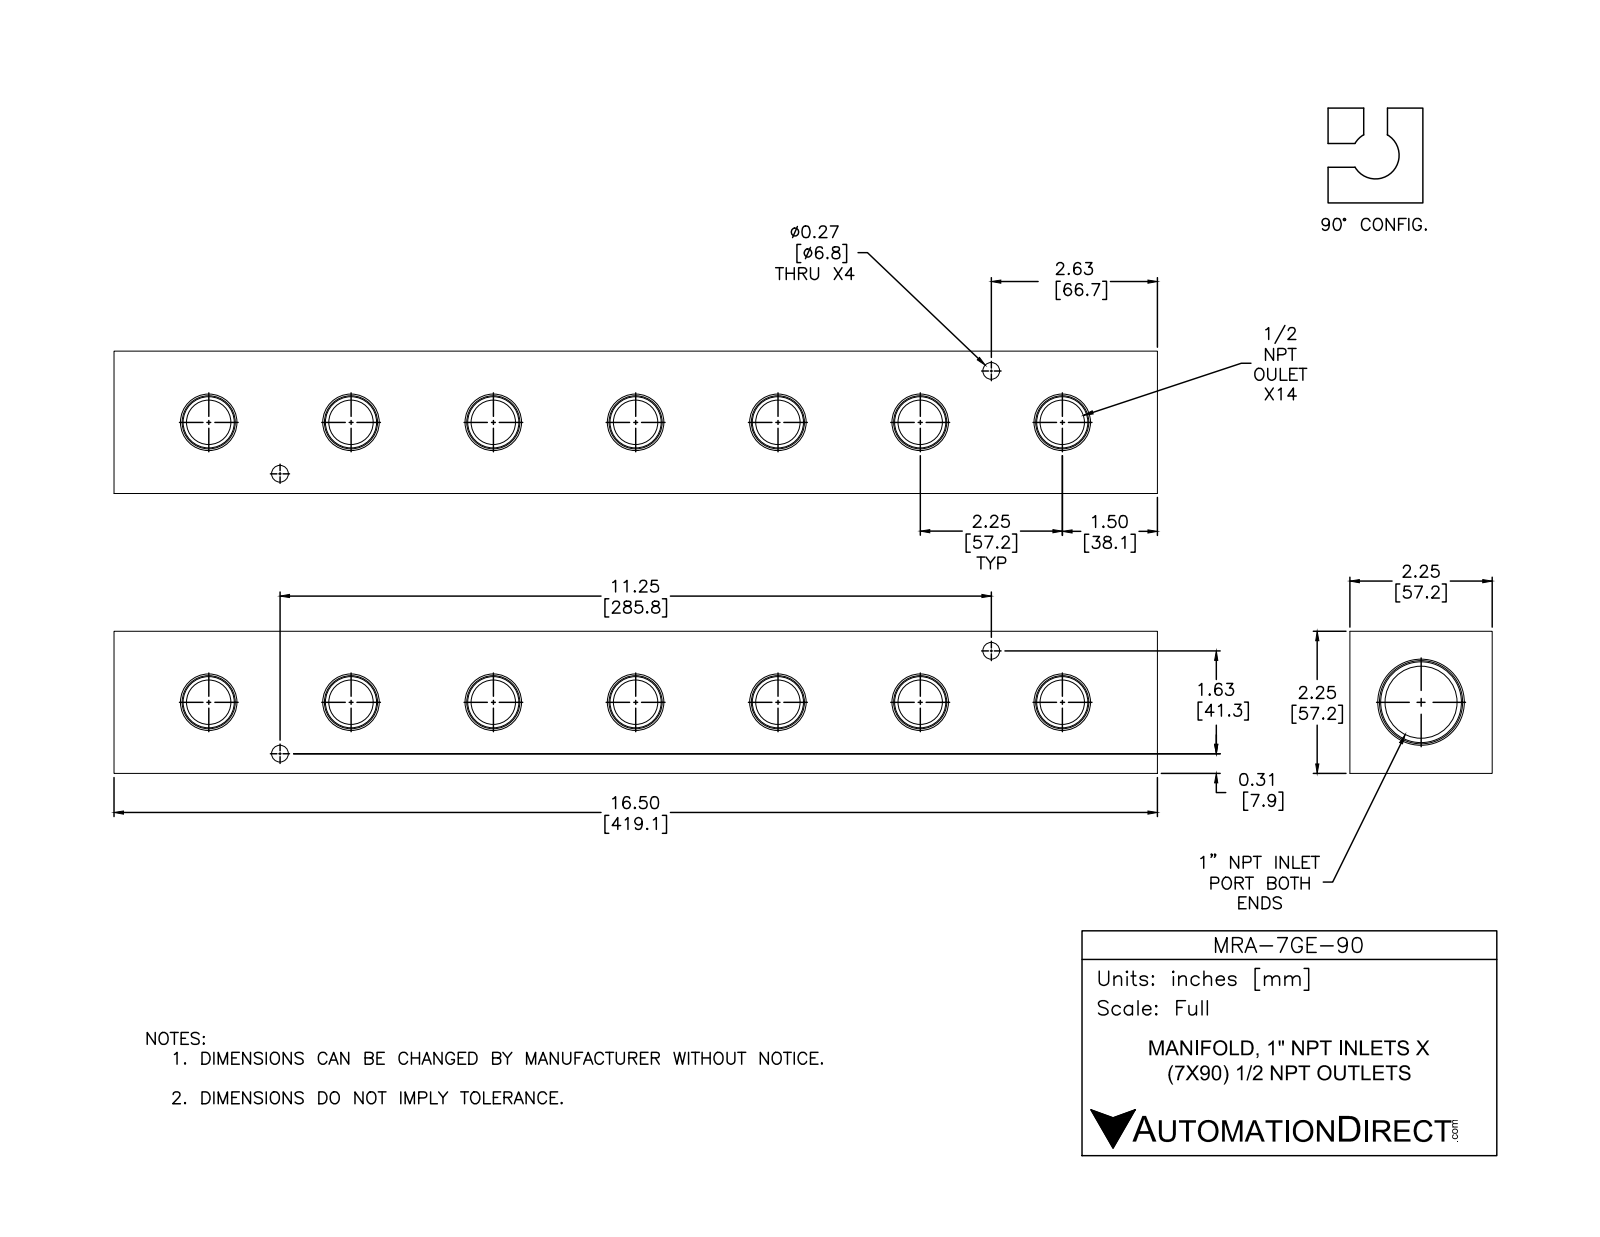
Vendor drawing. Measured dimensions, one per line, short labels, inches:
name: MRA-7GE-90
written by: SolidWorks 2015 (CONFIG_CONTROL_DESIGN)
unit: in
bodies: 1 solid, 132 faces (22 planar, 46 cylindrical, 64 other)
size: 16.5 × 2.25 × 2.25
volume: 61.52 in³; area: 232.2 in²
holes: 14× ⌀0.703, 4× ⌀0.266, 1× ⌀1.141
face distances: 2.25, 16.5, 0.53, 1.72, 0.66, 15.84, 15.18
hole spacings: 2.25, 4.5, 1.388, 6.75, 9, 3.472, 5.683, 7.917
